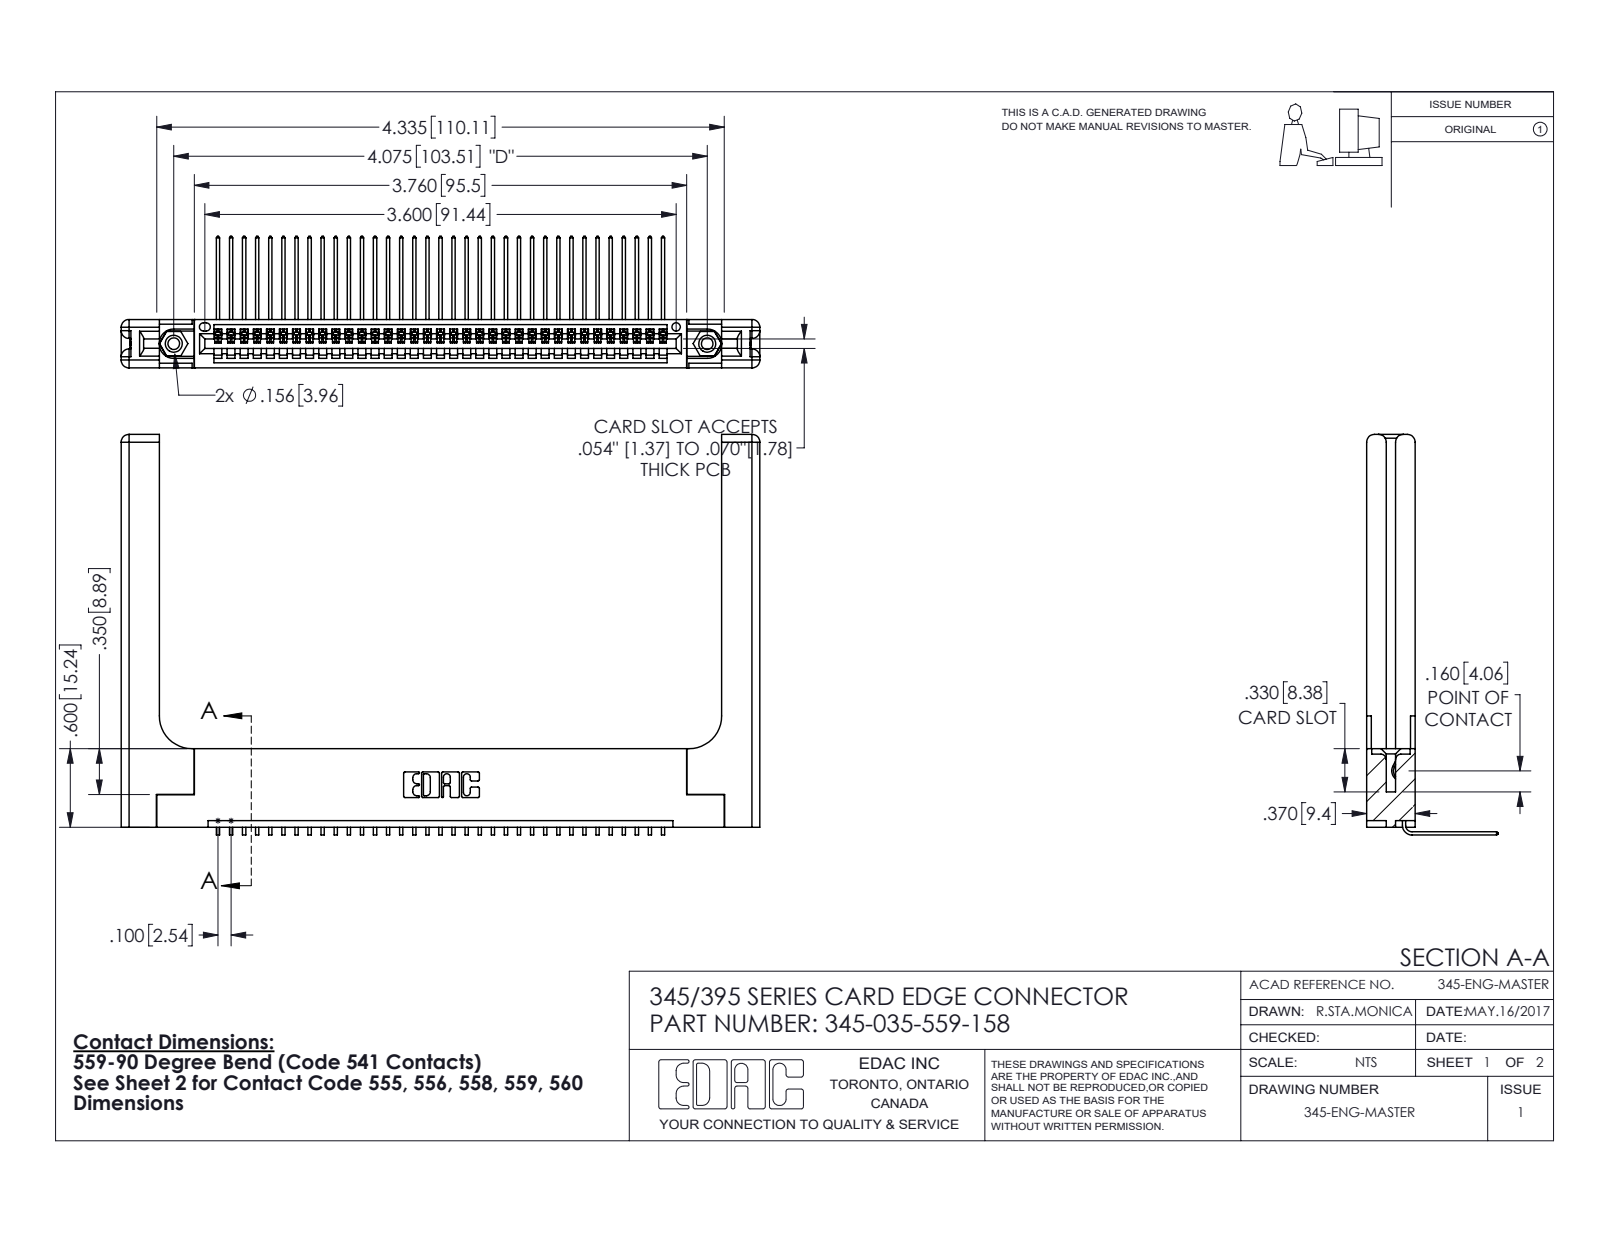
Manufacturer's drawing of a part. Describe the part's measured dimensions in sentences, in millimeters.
The part is named "345-292-001_558 559 Tail - 1; 345-035-559-158; 345 Part_Flush Mounting Lugs - 0.156 Dia-TH; 345-250-001_345-250-001-102 (+1 more)". Its 3-D file was written by "SolidWorks 2016 (CONFIG_CONTROL_DESIGN)". It is 40 solids with 2482 faces: 1698 planar, 724 cylindrical and 60 other. Overall it measures 123.9 by 77.7 by 25.5 millimeters. Its volume is 20 340 cubic millimeters and its surface area 21 620 square millimeters. Round holes: 2 of diameter 2.3, 2 of diameter 3.2, 2 of diameter 4, 1 of diameter 1.6. Round bosses or shafts: 2 of diameter 3.9. Partial cylindrical surfaces (rounded edges, fillets, slot ends): 70 of radius 0.2, 22 of radius 0.3, 16 of radius 1.5, 6 of radius 0.2, 6 of radius 0.8, 3 of radius 0.7, 2 of radius 0.8, 2 of radius 0.8. The main face-to-face distances are 9.4, 1.8, 7.6, 5.1, 2.5, 6.9, 0.6, 3.8, 3.8, 5.7. The hole center spacings are 6.9, 97.5, 103.5.
